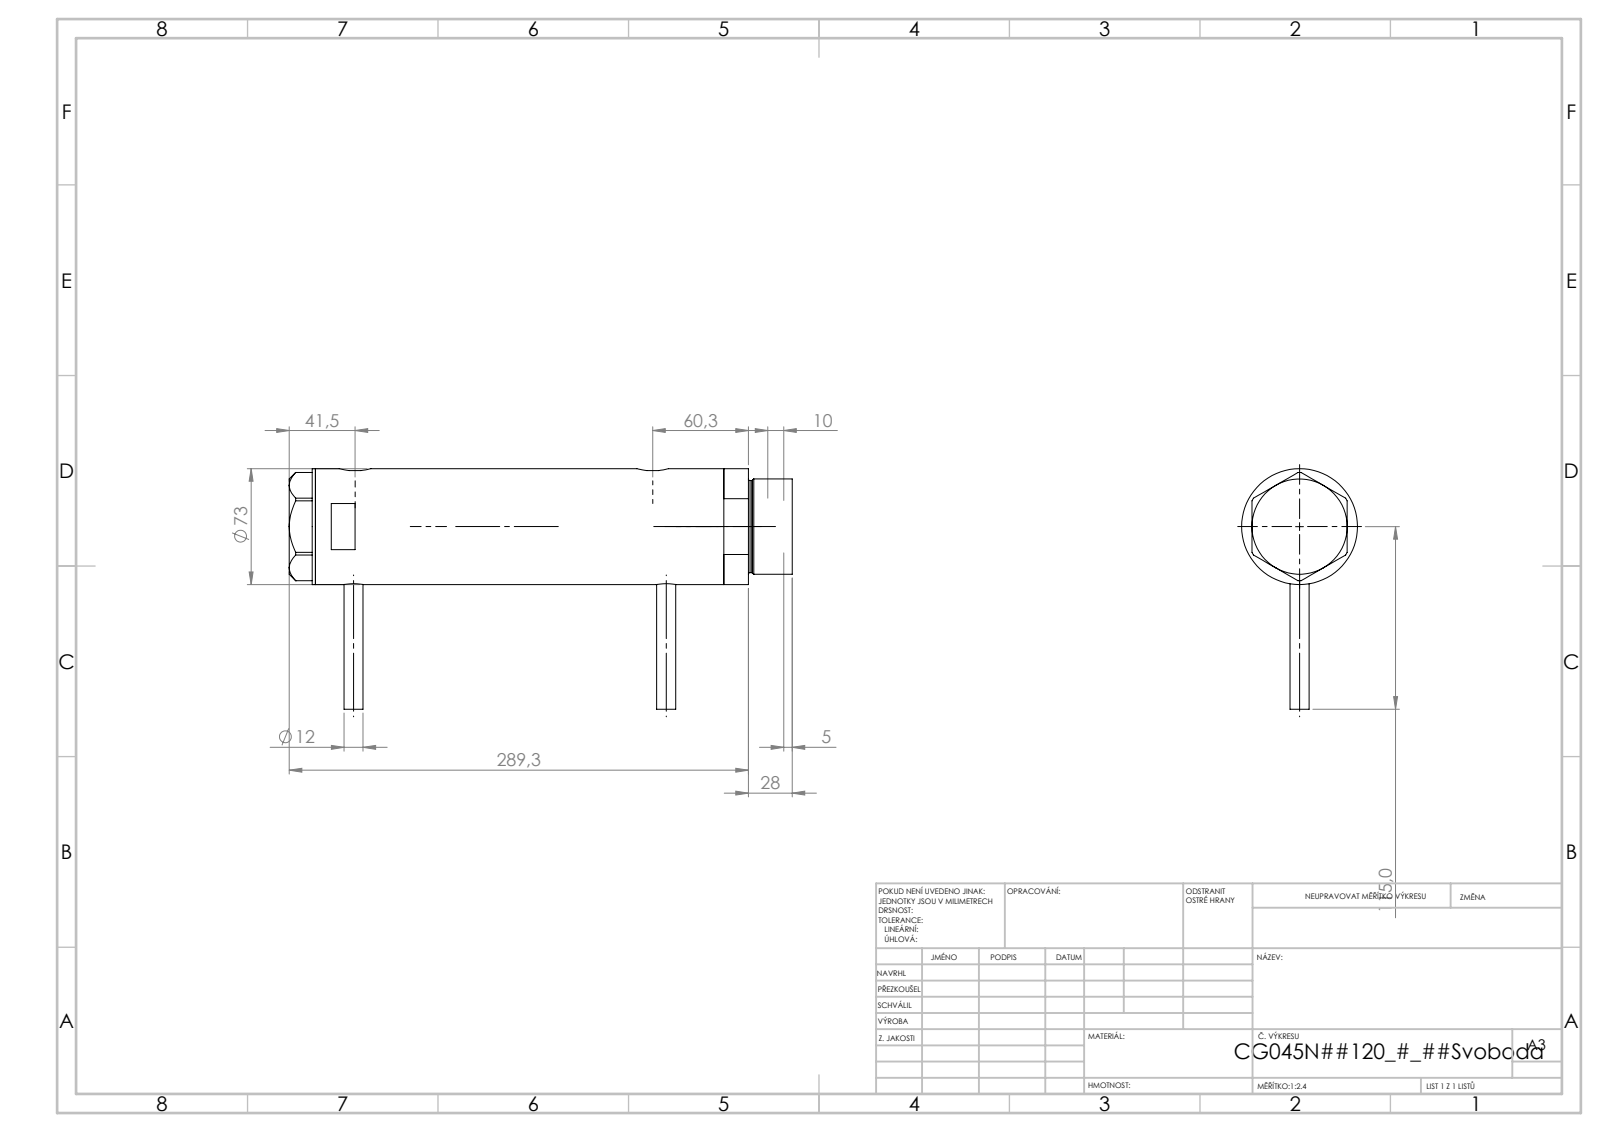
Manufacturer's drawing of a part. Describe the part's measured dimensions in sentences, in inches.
The part is named "V270CG_BACK; V270CG_MIDDLE; V270CG_VC; V270CG_FRONT". Its 3-D file was written by "SolidWorks 2019 (CONFIG_CONTROL_DESIGN)". It is 4 solids with 125 faces: 50 planar, 55 cylindrical and 20 other. Overall it measures 12.475 by 5.965 by 2.874 inches. Its volume is 70.48 cubic inches and its surface area 300.9 square inches. Round holes: 2 of diameter 0.197, 2 of diameter 0.492, 2 of diameter 0.518, 1 of diameter 0.413, 1 of diameter 1.26, 1 of diameter 1.319, 1 of diameter 1.772, 1 of diameter 1.89, 1 of diameter 2.52. Round bosses or shafts: 2 of diameter 0.472, 1 of diameter 2.874, 1 of diameter 2.362, 1 of diameter 2.283, 1 of diameter 1.22. Partial cylindrical surfaces (rounded edges, fillets, slot ends): 2 of radius 0.394. The main face-to-face distances are 8.366, 1.024, 7.343, 0.65, 1.673, 9.016, 0.079, 11.826, 12.475, 10.802. The hole center spacings are 0.039, 0.335, 7.382, 7.421, 7.717, 7.756.
